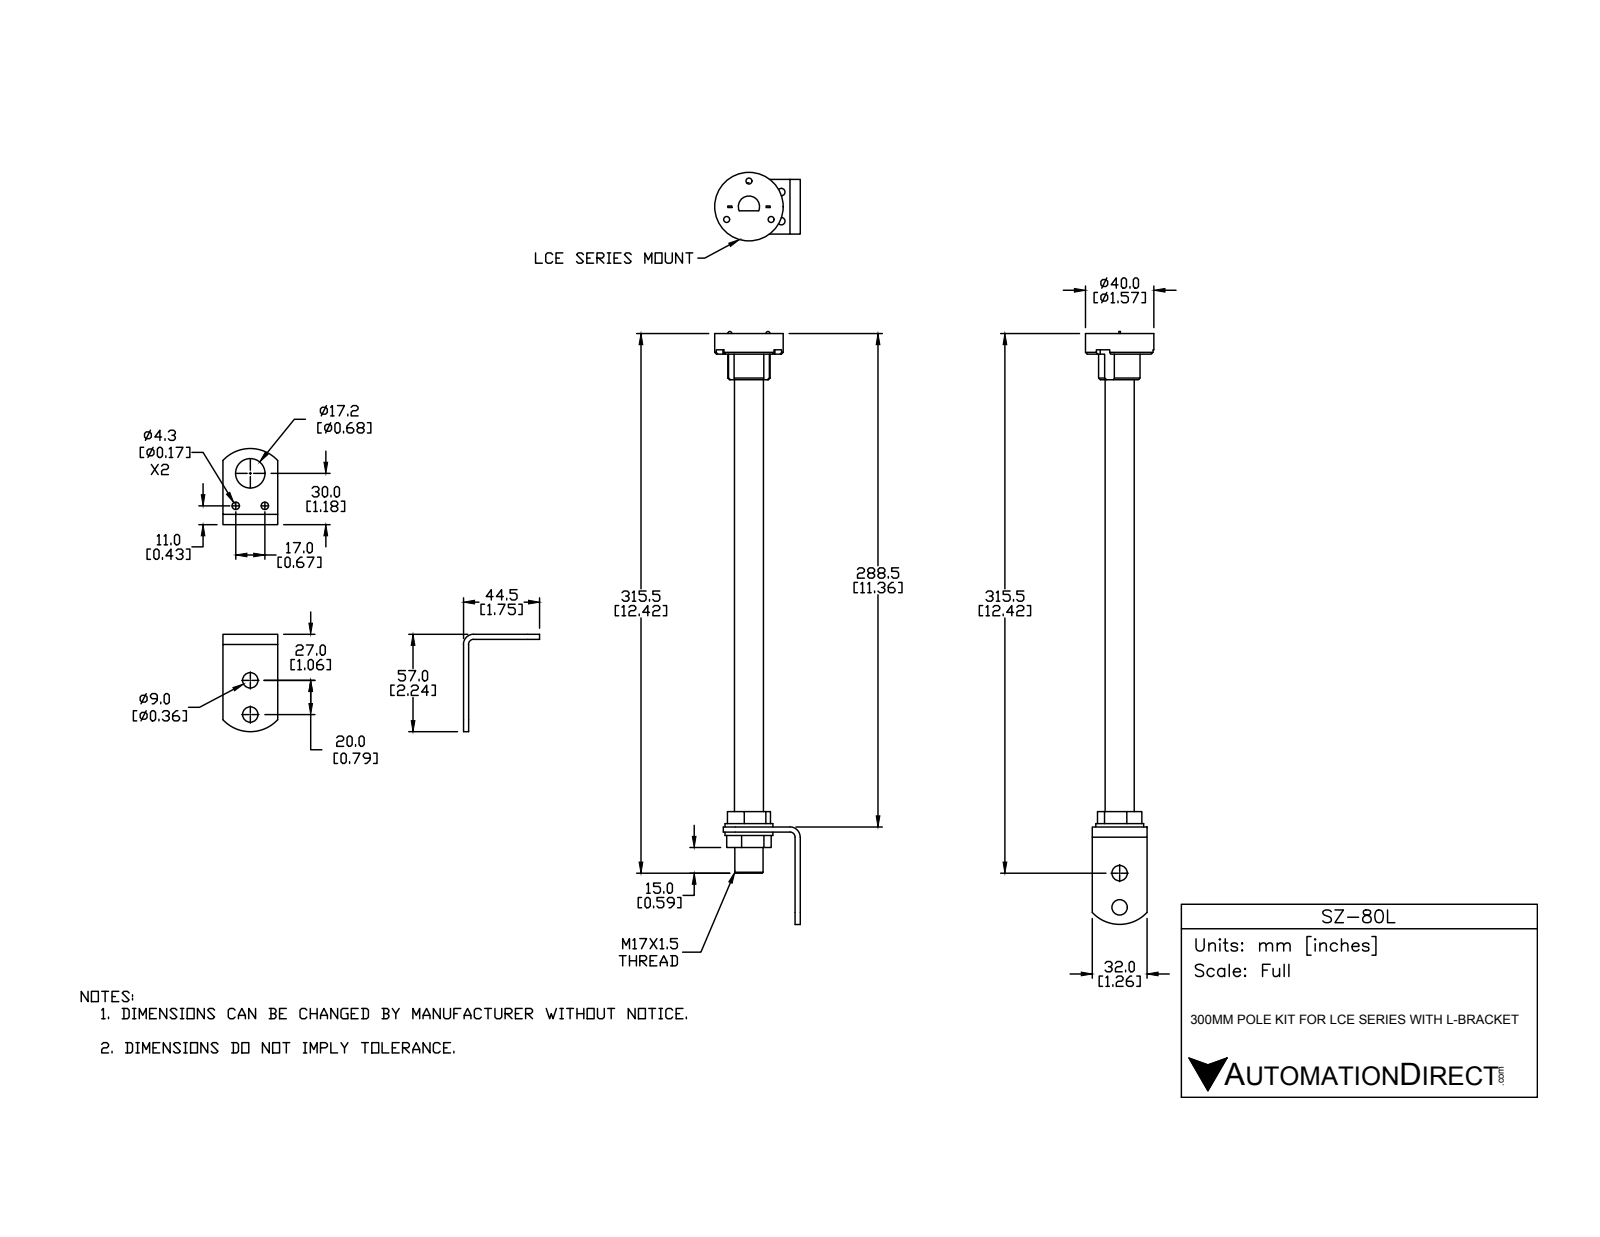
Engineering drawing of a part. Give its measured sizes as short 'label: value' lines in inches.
name: SZ-80L-WASHER; SZ-80L-NUT; SZ-80L-POLE; B22220020-F1 (+2 more)
written by: SolidWorks 2016 (AUTOMOTIVE_DESIGN)
unit: in
bodies: 7 solids, 122 faces (53 planar, 59 cylindrical, 10 other)
size: 13.65 × 1.969 × 1.575
volume: 3.577 in³; area: 72.69 in²
holes: 3× ⌀0.138, 2× ⌀0.169, 2× ⌀0.356, 1× ⌀0.496, 1× ⌀0.65, 1× ⌀0.677, 1× ⌀0.689
bosses: 1× ⌀1.575, 1× ⌀1.102, 1× ⌀0.669
rounds: 3× R0.177, 3× R0.256, 2× R0.047, 2× R0.858, 1× R0.118, 1× R0.236, 1× R0.244, 1× R0.362
face distances: 0.118, 11.358, 0.197, 0.079, 11.476, 0.276, 0.472, 11.004, 11.555, 11.28
hole spacings: 0.591, 1.023, 0.819, 0.24, 0.669, 0.673, 0.787, 0.791
